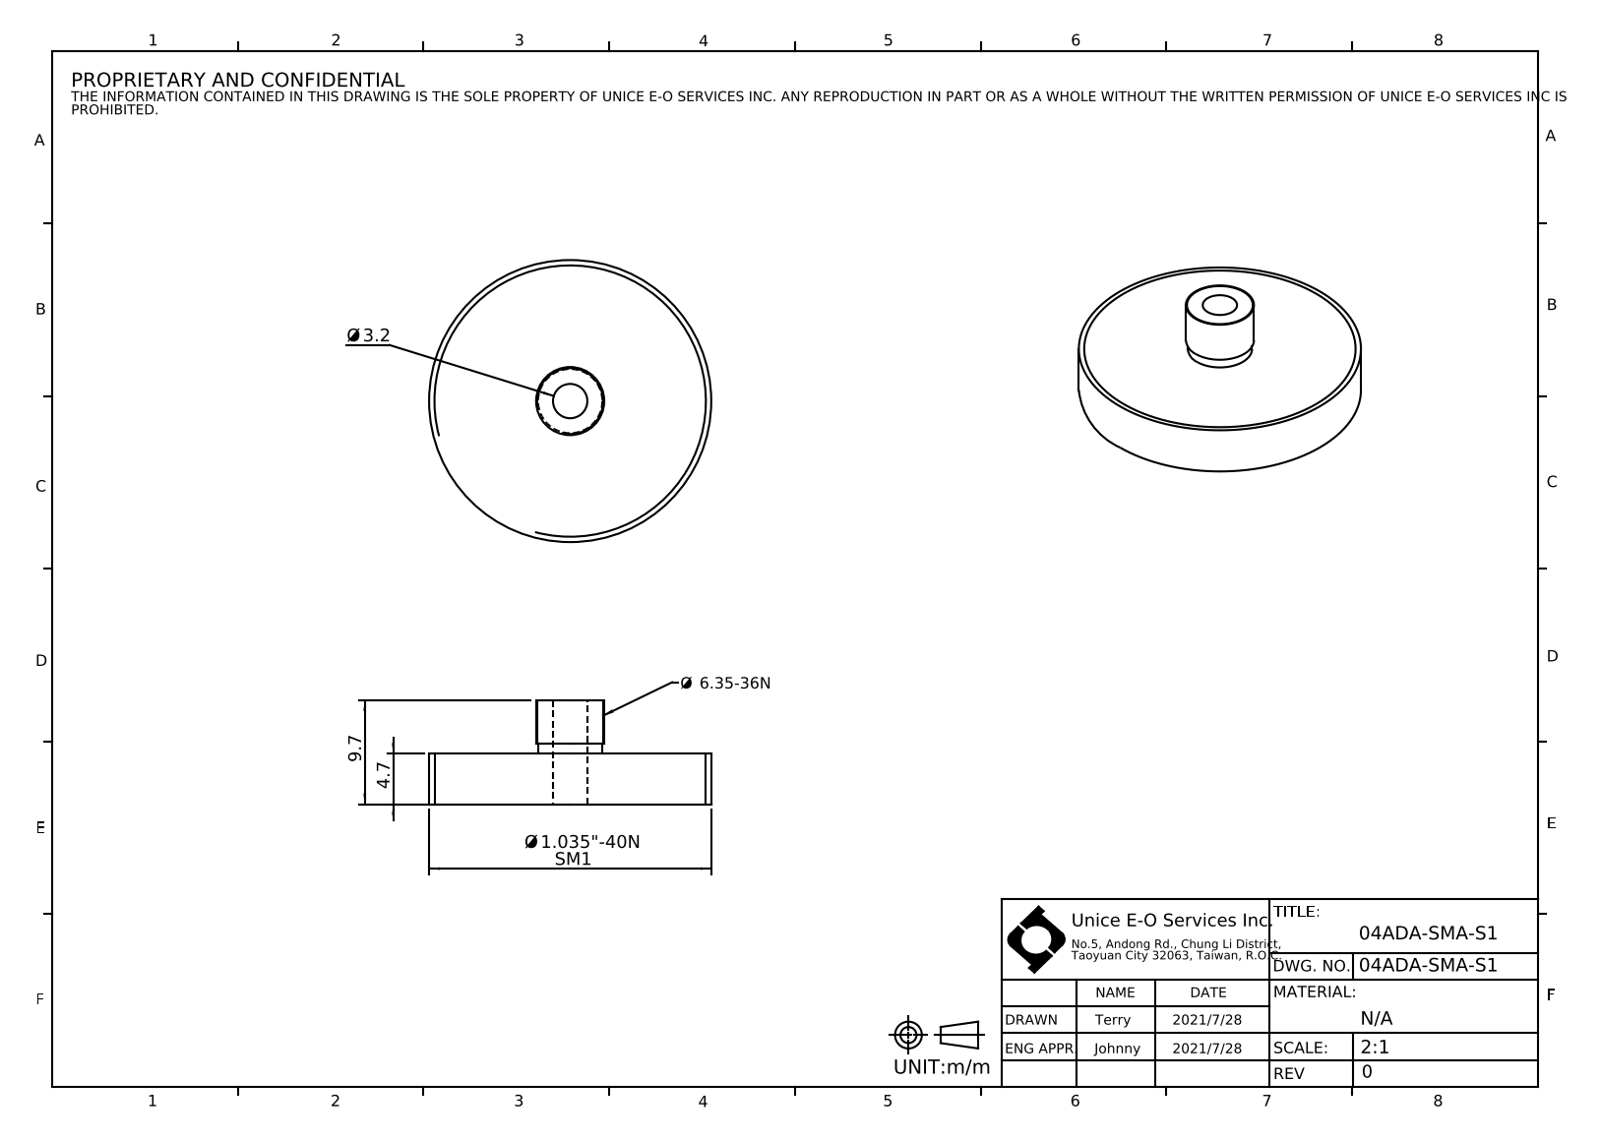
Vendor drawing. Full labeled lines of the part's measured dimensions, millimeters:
Part name (STEP PRODUCT): 04ADA-SMA-S1
STEP written by: SolidWorks 2020 (CONFIG_CONTROL_DESIGN)
Units: millimetres
Bodies: 1 solid, 46 faces (4 planar, 18 cylindrical, 24 other)
Overall size (bounding box): 26.3 × 26.3 × 9.7
Volume: 2 564 mm³ · Surface area: 1 862 mm²
Round holes (diameter × count): ⌀3.2 ×1
Round bosses / shafts (diameter × count): ⌀26.3 ×1, ⌀6.35 ×1, ⌀6 ×1
Main face-to-face distances: 4.7, 9.7, 5, 5.7, 1, 4
